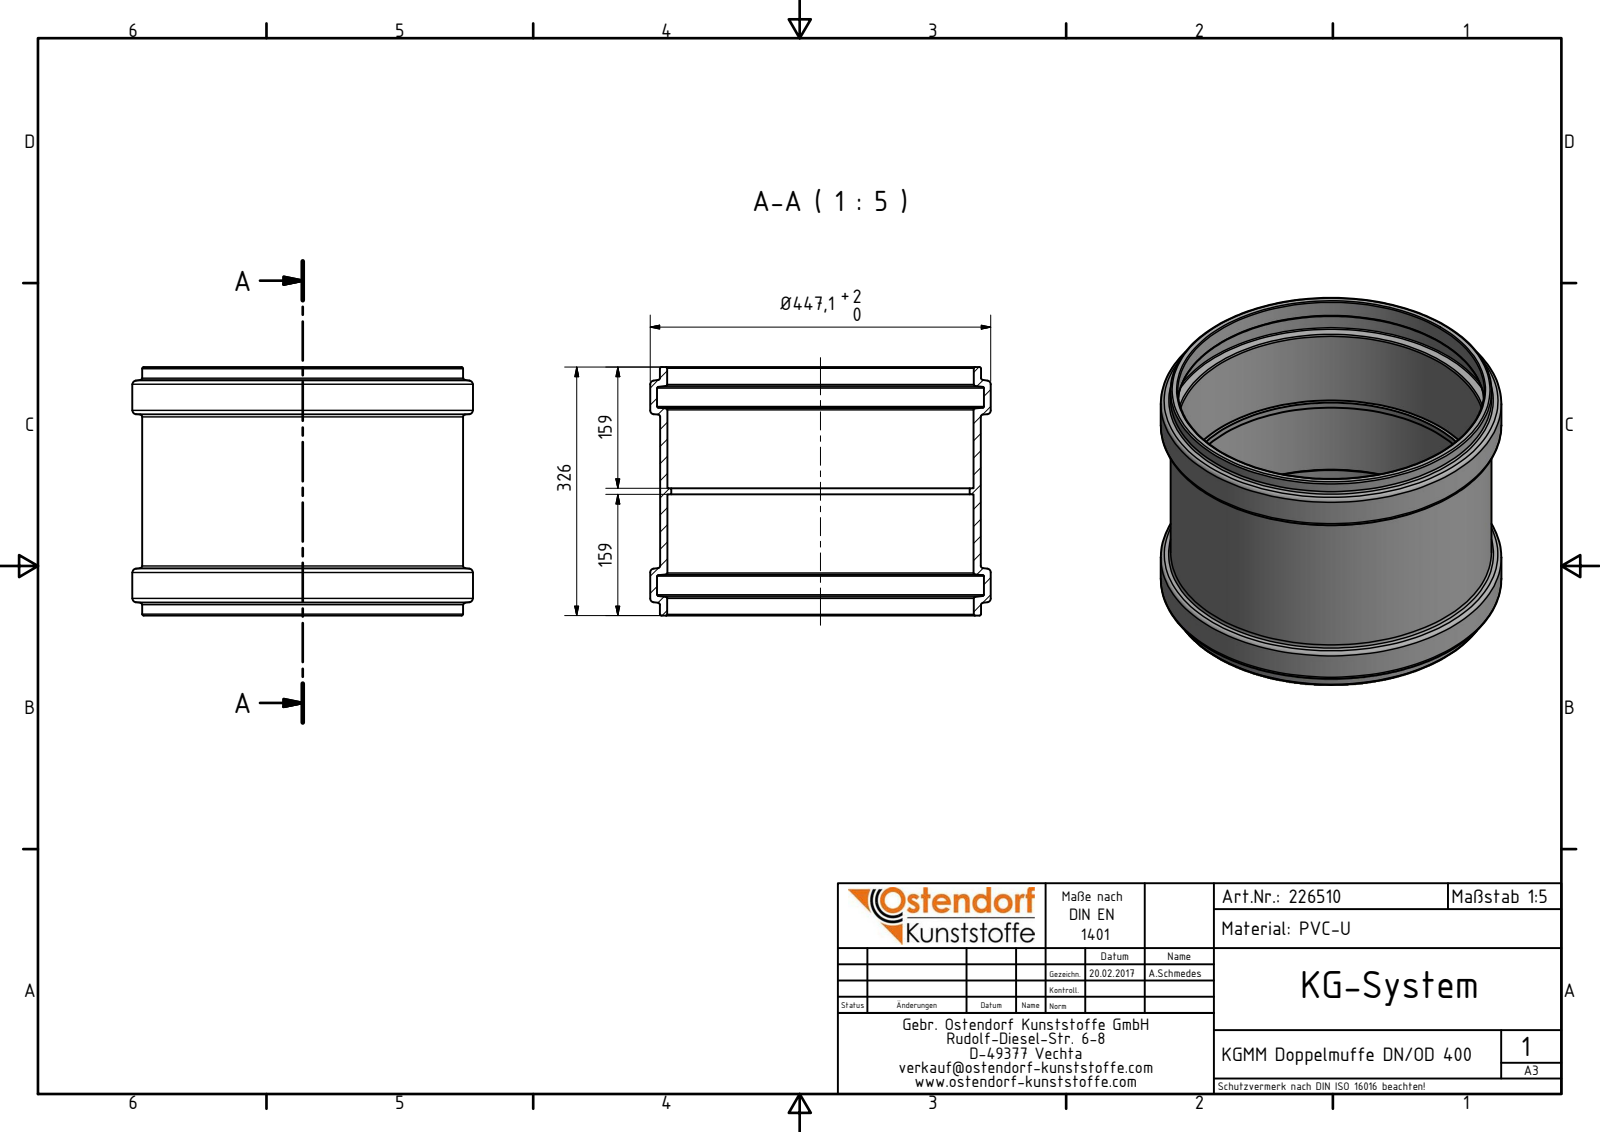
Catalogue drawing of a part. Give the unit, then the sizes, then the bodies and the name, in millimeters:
Units: millimetres
Overall size (bounding box): 447.1 × 447.1 × 326
Round holes (diameter × count): ⌀392 ×1, ⌀402 ×1, ⌀402.4 ×1, ⌀429.1 ×1
Round bosses / shafts (diameter × count): ⌀447.1 ×1, ⌀421.4 ×1, ⌀421.1 ×1
Main face-to-face distances: 159, 167, 326, 8
Volume: 4 623 000 mm³ · Surface area: 994 460 mm²
Bodies: 1 solid, 44 faces (4 planar, 12 cylindrical, 28 other)
Part name (STEP PRODUCT): 226510 KGMM Doppelmuffe DN_OD 400
STEP written by: Autodesk Inventor 2016 (AUTOMOTIVE_DESIGN)
